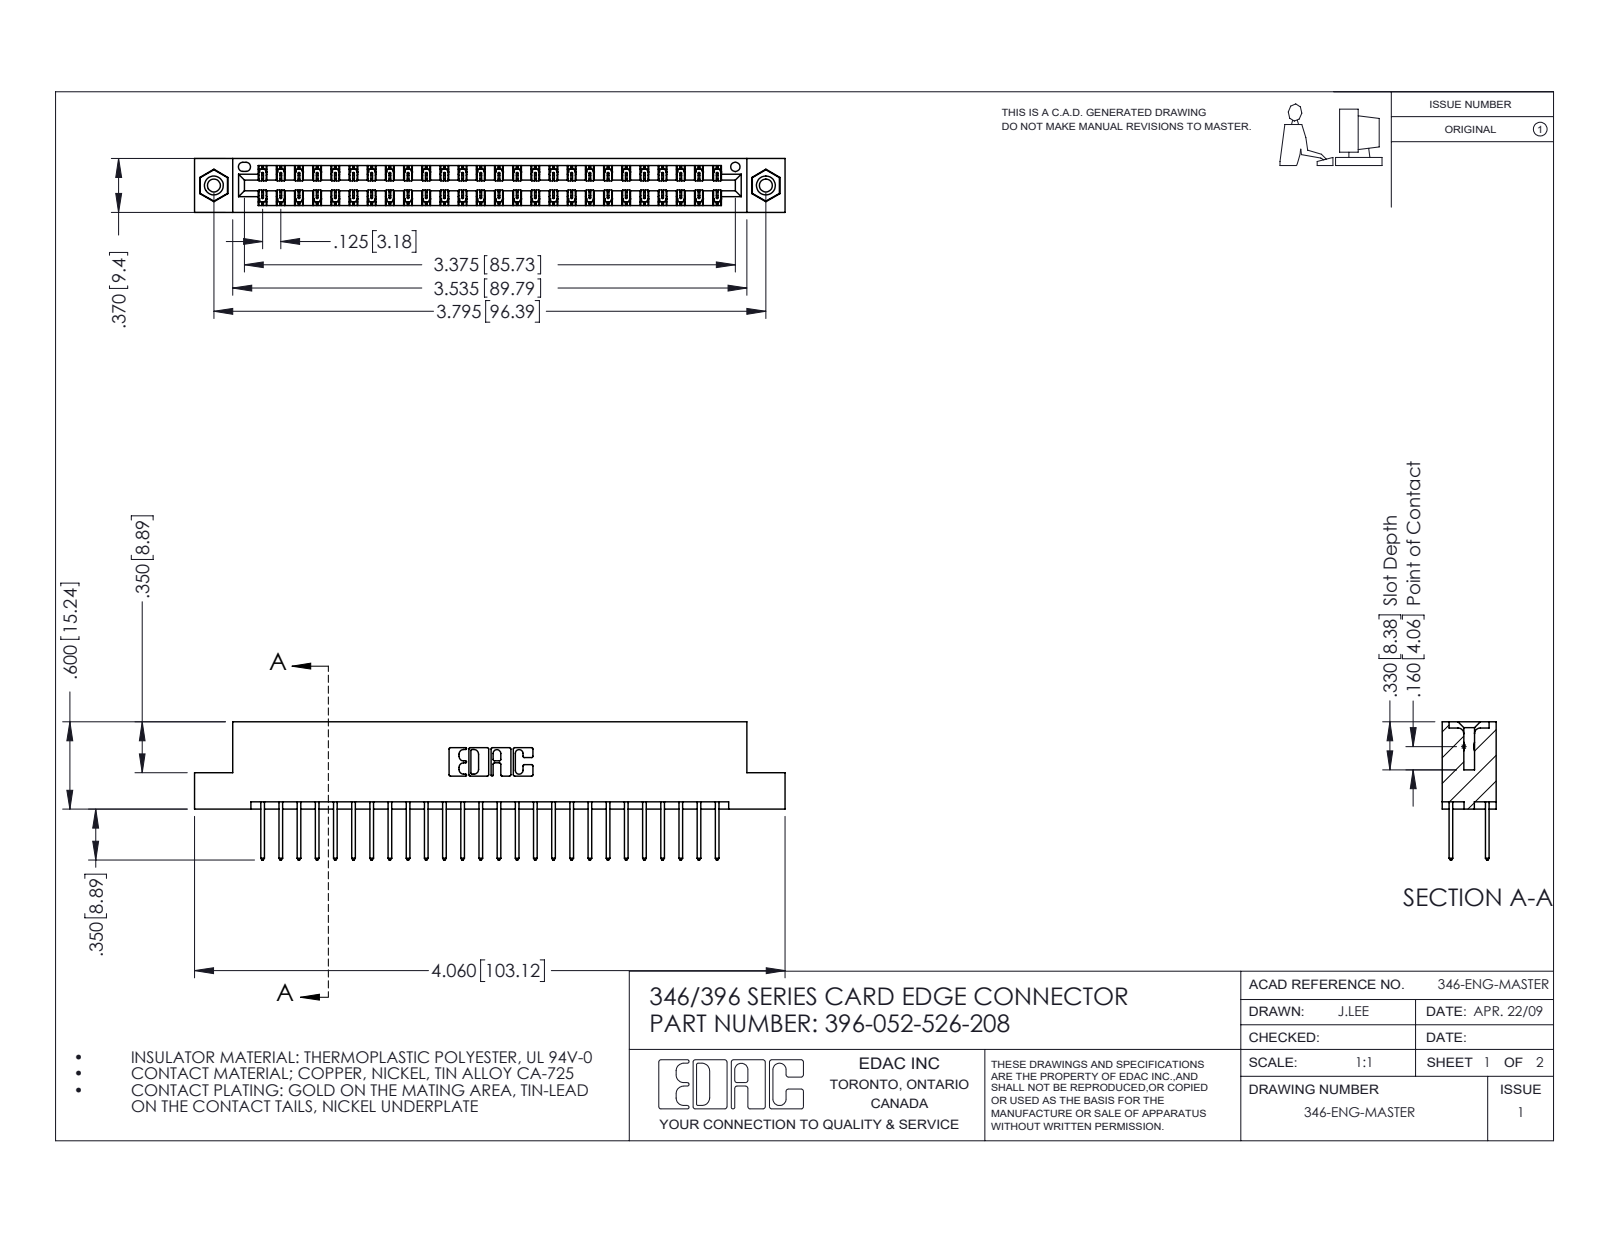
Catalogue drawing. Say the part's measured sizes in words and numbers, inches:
The part is named "396-052-526-208; 345-250-001_345-250-003-102; 345-292-001_345-293-126; 346 Part_Flush Mounting Lugs - 0.156 Dia-TI". Its 3-D file was written by "SolidWorks 2016 (CONFIG_CONTROL_DESIGN)". It is 55 solids with 2886 faces: 1928 planar, 942 cylindrical and 16 other. Overall it measures 4.06 by 0.95 by 0.37 inches. Its volume is 0.611 cubic inches and its surface area 21.56 square inches. Round holes: 2 of diameter 0.089, 2 of diameter 0.125, 2 of diameter 0.156, 1 of diameter 0.064. Round bosses or shafts: 2 of diameter 0.155. Partial cylindrical surfaces (rounded edges, fillets, slot ends): 78 of radius 0.006, 52 of radius 0.01, 22 of radius 0.01, 6 of radius 0.007, 6 of radius 0.031, 3 of radius 0.026, 2 of radius 0.014, 2 of radius 0.022. The main face-to-face distances are 0.048, 0.322, 0.25, 0.37, 0.072, 0.298, 0.025, 0.275, 0.148, 0.222. The hole center spacings are 0.246, 3.587, 3.795.
